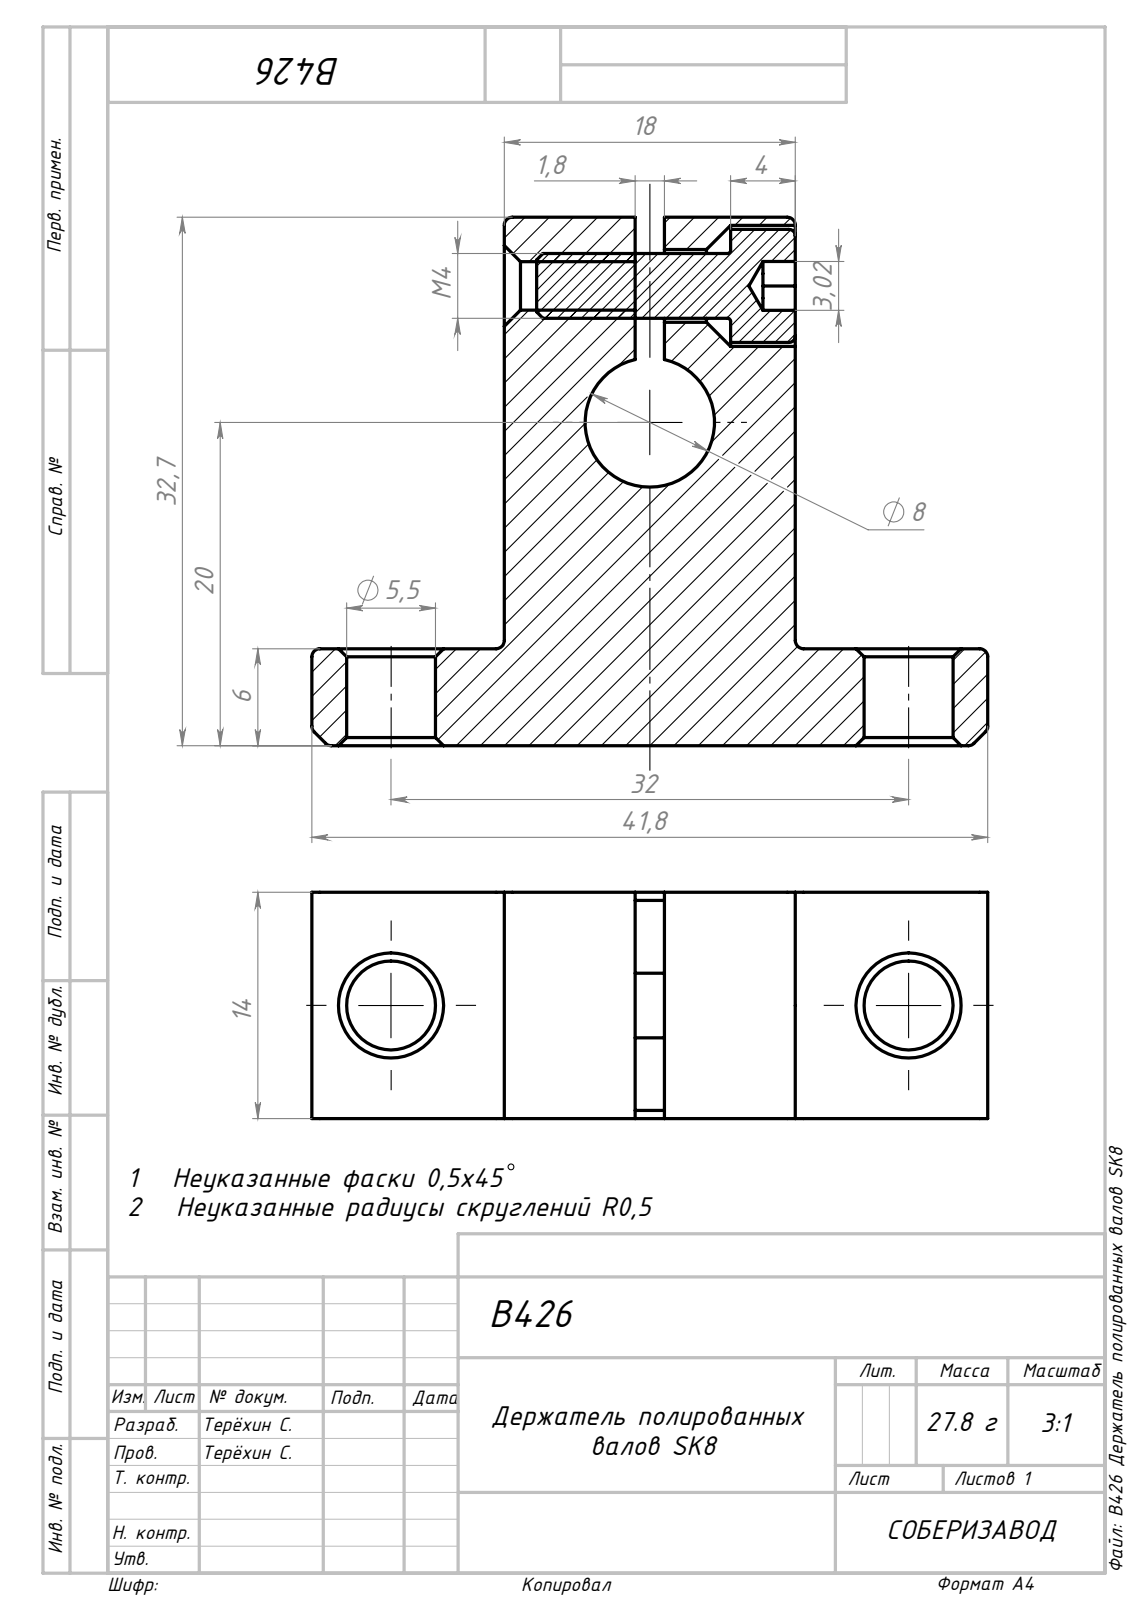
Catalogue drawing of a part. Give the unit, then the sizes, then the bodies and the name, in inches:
Units: inches
Overall size (bounding box): 1.646 × 1.287 × 0.551
Round holes (diameter × count): ⌀0.217 ×2, ⌀0.118 ×1, ⌀0.177 ×1, ⌀0.295 ×1, ⌀0.315 ×1
Round bosses / shafts (diameter × count): ⌀0.276 ×1, ⌀0.157 ×1
Partial cylindrical surfaces — rounded edges, fillets, slot ends (radius × count): R0.02 ×10
Main face-to-face distances: 0.551, 0.709, 0.236, 0.319, 0.39, 1.287, 1.051, 0.469, 0.787, 0.858
Hole centre spacings: 1.26
Volume: 0.547 in³ · Surface area: 6.983 in²
Bodies: 2 solids, 83 faces (30 planar, 27 cylindrical, 26 other)
Part name (STEP PRODUCT): B426 Держатель полированных валов SK8_00; Сборка5; socket head cap screw_din_DIN 912 M4 x 12 --- 12N
STEP written by: SolidWorks 2024 (AUTOMOTIVE_DESIGN)
